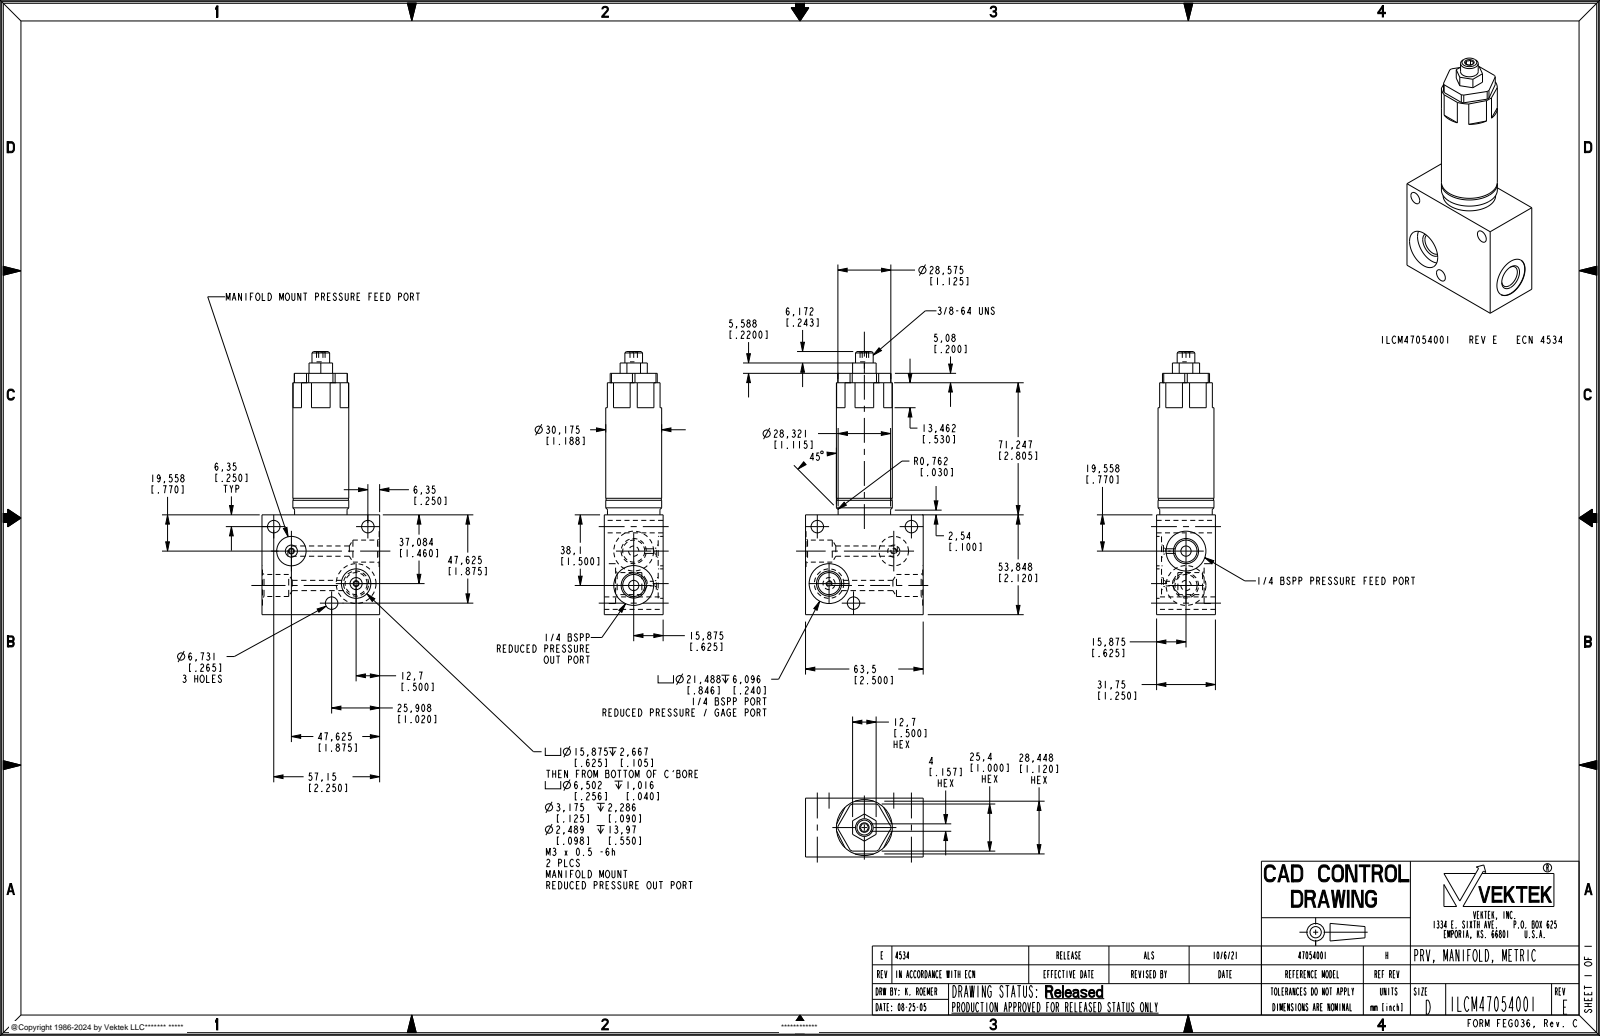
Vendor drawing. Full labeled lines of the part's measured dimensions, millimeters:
Part name (STEP PRODUCT): ILCM47054001
STEP written by: PRO/ENGINEER BY PARAMETRIC TECHNOLOGY CORPORATION, 2007460 (AUTOMOTIVE_DESIGN_CC2)
Units: millimetres
Bodies: 1 solid, 134 faces (54 planar, 58 cylindrical, 22 other)
Overall size (bounding box): 148.16 × 63.5 × 31.75
Volume: 153 554 mm³ · Surface area: 29 365 mm²
Round holes (diameter × count): ⌀6.73 ×3, ⌀11.89 ×3, ⌀21.49 ×3, ⌀2.49 ×2, ⌀3.17 ×2, ⌀5.54 ×2, ⌀6.5 ×2, ⌀15.88 ×2
Round bosses / shafts (diameter × count): ⌀13.16 ×3, ⌀30.18 ×1, ⌀28.32 ×1, ⌀9.53 ×1
Partial cylindrical surfaces — rounded edges, fillets, slot ends (radius × count): R14.29 ×1
Main face-to-face distances: 31.76, 53.85, 63.5, 63.25, 136.4, 82.55, 2.67, 29.09, 25.4, 1.66
Hole centre spacings: 16.28, 16.9, 18.54, 31.38, 35.48, 39.08, 43.34, 45.67
